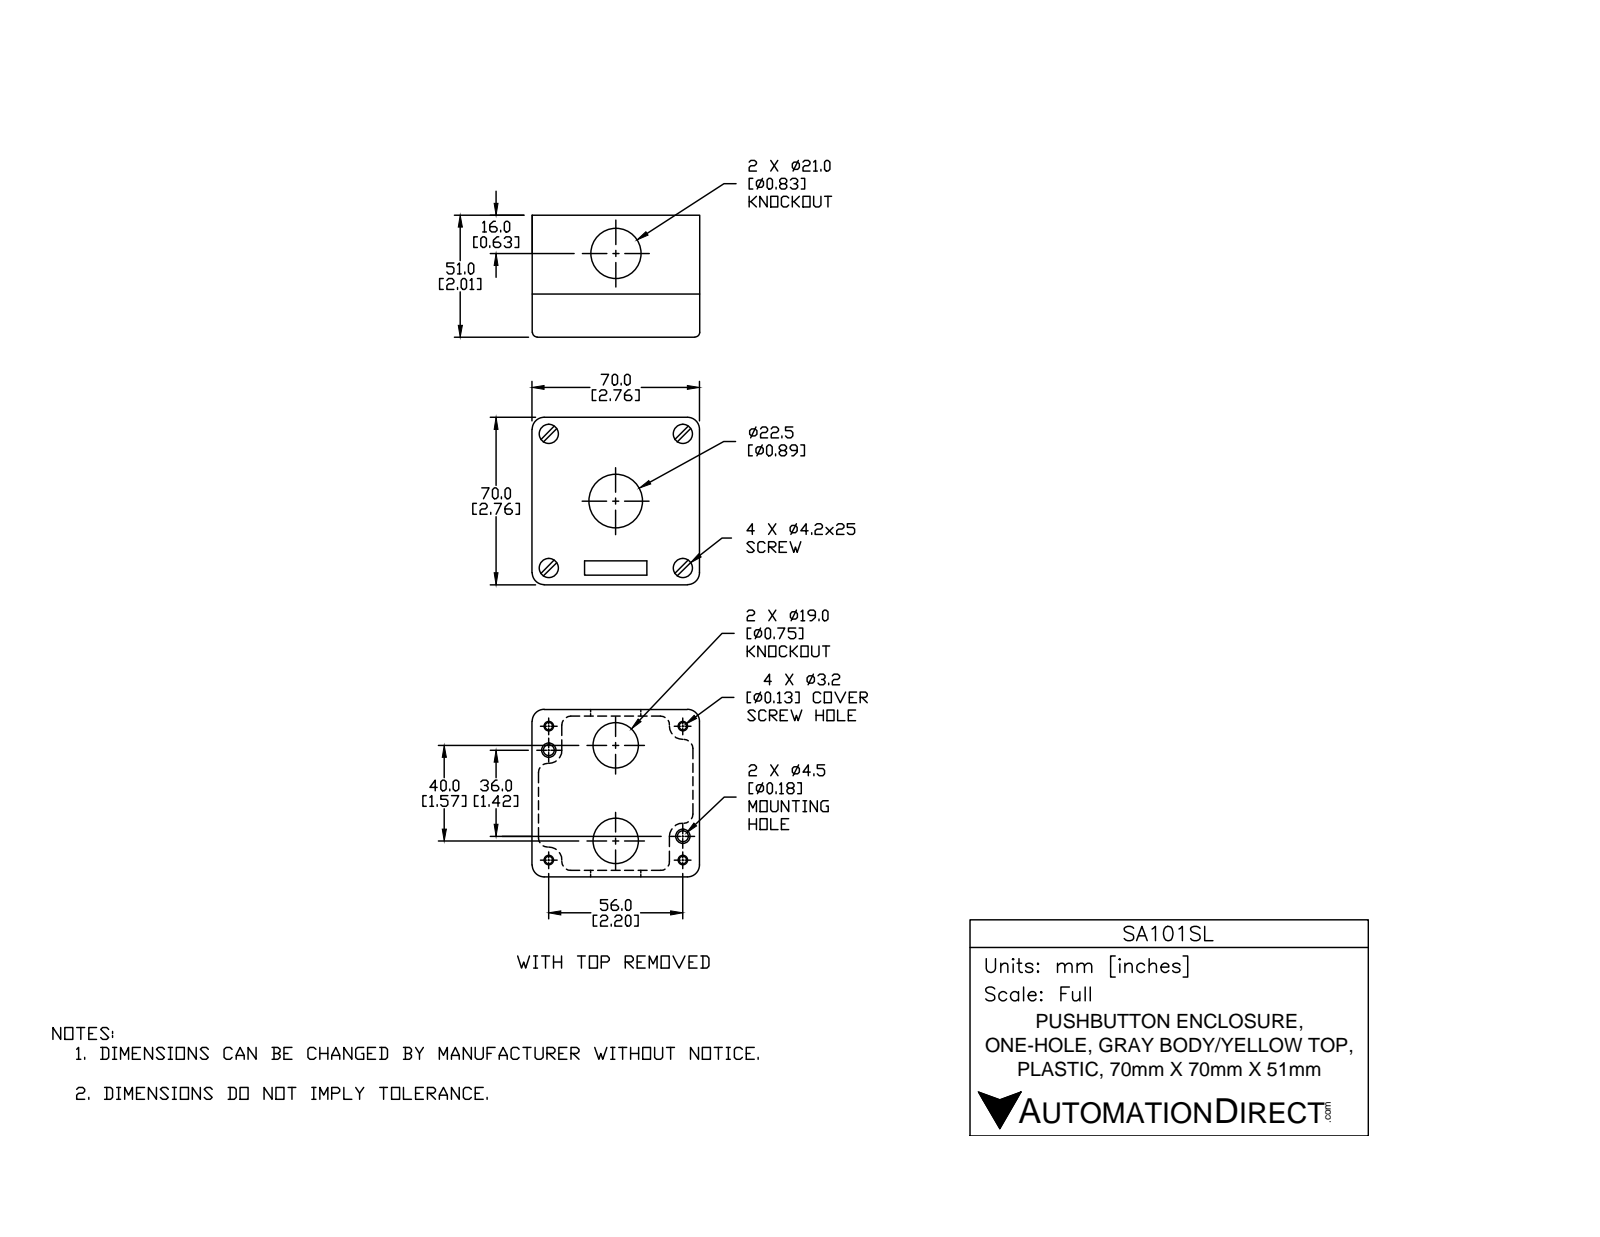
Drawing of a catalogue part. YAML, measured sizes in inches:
part_name: "SA101SL"
step_written_by: "SolidWorks 2019 (AUTOMOTIVE_DESIGN)"
units: inches
bodies: {solids: 6, faces: 450, planar: 121, cylindrical: 178, other: 151}
overall_size: [2.756, 2.756, 1.965]
volume: 5.225
surface_area: 74.07
round_holes:
  - {diameter: 0.126, count: 4}
  - {diameter: 0.165, count: 4}
  - {diameter: 0.315, count: 4}
  - {diameter: 0.177, count: 2}
  - {diameter: 0.295, count: 2}
  - {diameter: 0.748, count: 2}
  - {diameter: 0.827, count: 1}
  - {diameter: 0.886, count: 1}
round_bosses_or_shafts:
  - {diameter: 0.291, count: 4}
  - {diameter: 0.11, count: 4}
partial_cylinders:
  - {radius: 0.02, count: 16}
  - {radius: 0.041, count: 8}
  - {radius: 0.095, count: 8}
  - {radius: 0.039, count: 4}
  - {radius: 0.071, count: 4}
  - {radius: 0.197, count: 4}
  - {radius: 0.259, count: 4}
  - {radius: 0.323, count: 4}
face_to_face_distances: [2.756, 0.102, 2.654, 1.961, 0.087, 1.874, 0.079, 1.882, 1.795, 0.215]
hole_center_spacings: [1.146, 1.559, 2.188, 2.205, 0.394, 0.787, 1.105, 1.311]
